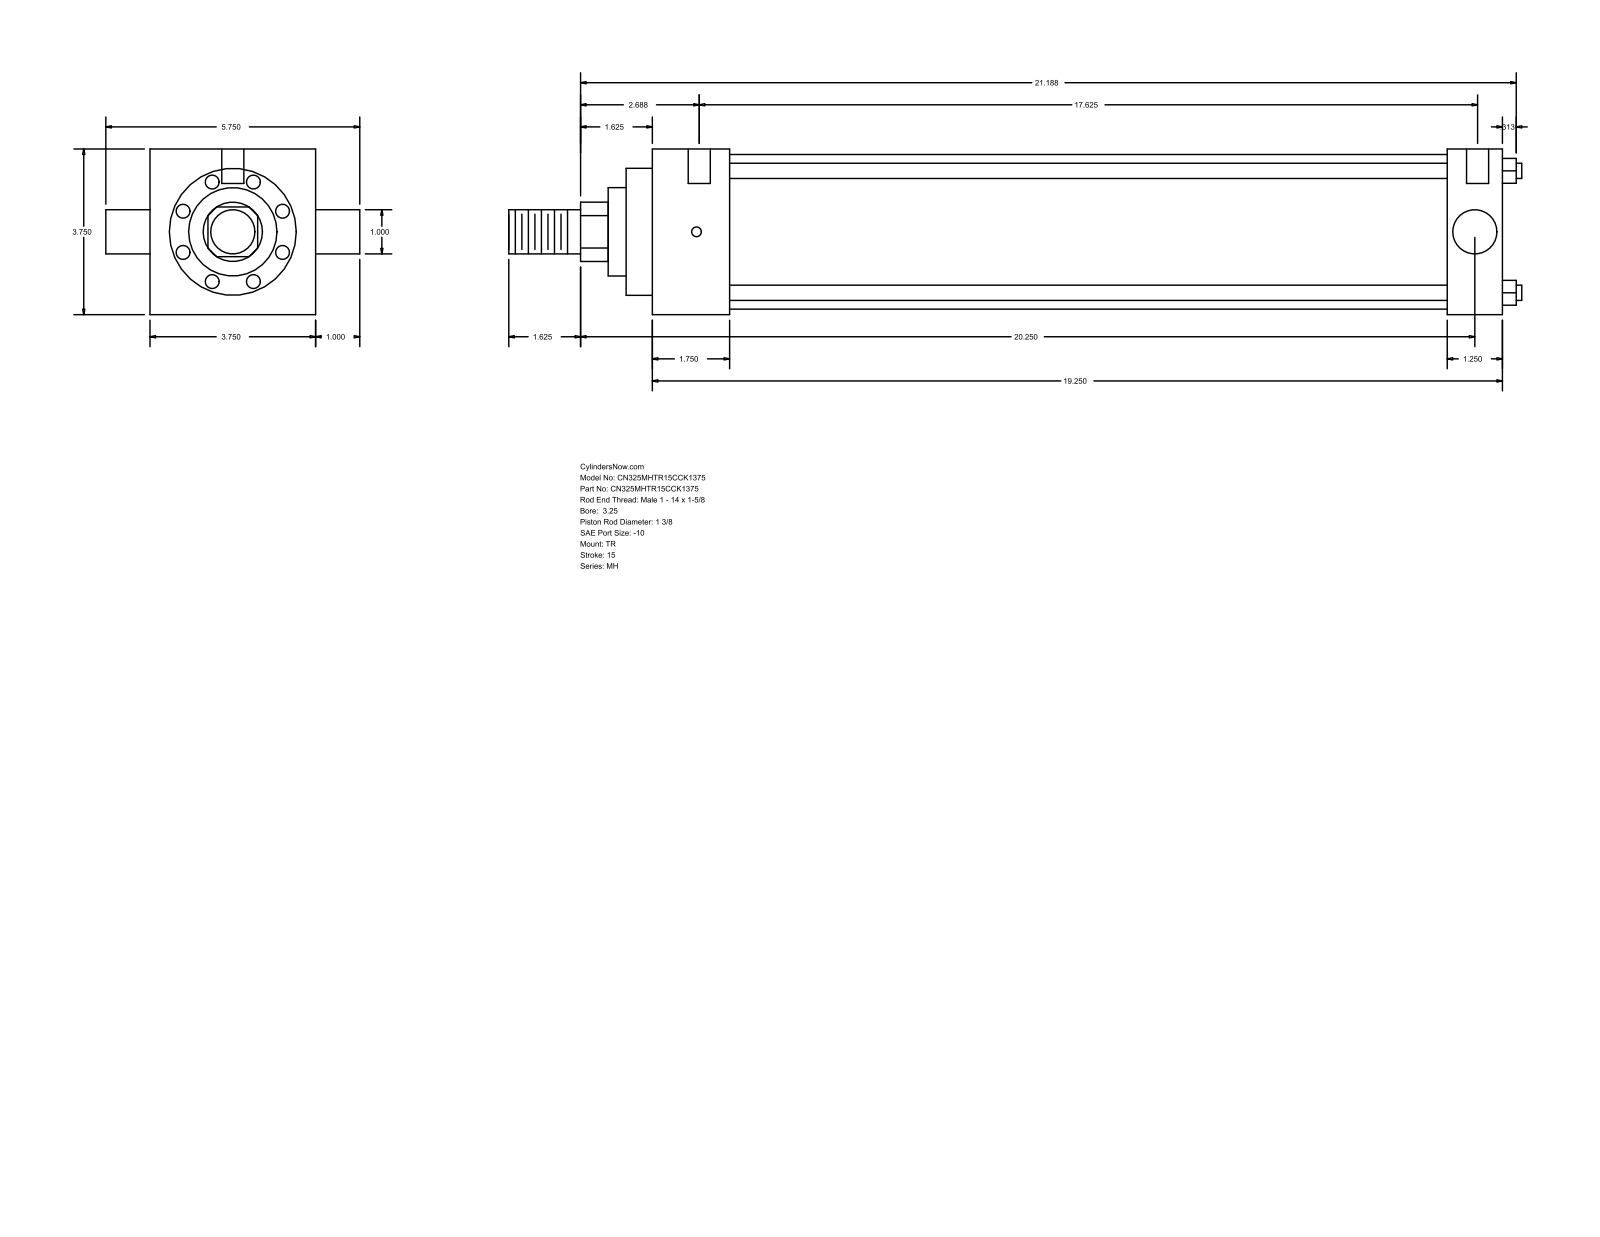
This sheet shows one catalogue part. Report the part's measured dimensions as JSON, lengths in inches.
{"part_name": "MH_TR__0325_1.375", "step_written_by": "GSSL Pune (CONFIG_CONTROL_DESIGN)", "units": "inches", "bodies": {"solids": 0, "faces": 86, "planar": 61, "cylindrical": 25, "other": 0}, "overall_size": [22.937, 5.75, 3.75], "round_holes": [[0.219, 3], [0.5, 2]], "round_bosses_or_shafts": [[0.345, 4], [1, 2], [3.5, 1], [2.875, 1], [2, 1], [1.375, 1]], "partial_cylinders_radius": [[0.672, 1]], "face_to_face_distances": [3.75, 19.25, 1.75, 18, 16.25, 17.5, 1.25, 0.594, 2.344, 18.594], "hole_center_spacings": [0.063, 0.187, 17.625, 17.688, 17.813, 17.875]}
